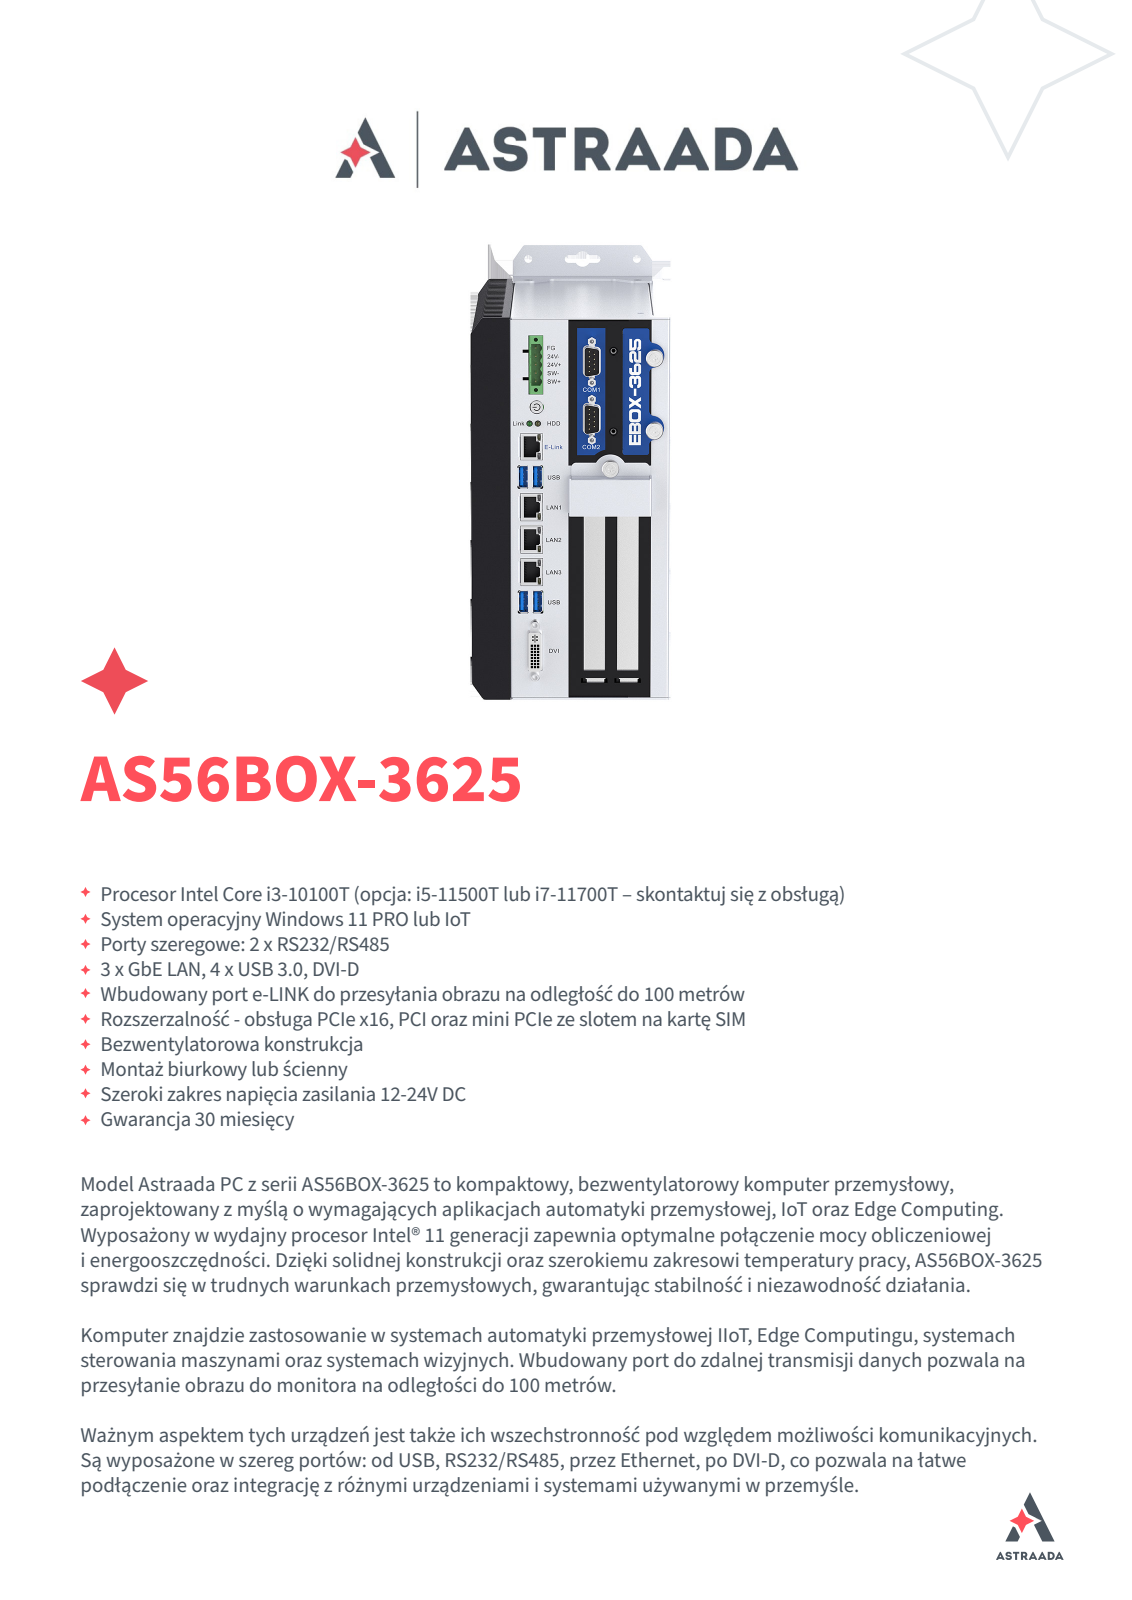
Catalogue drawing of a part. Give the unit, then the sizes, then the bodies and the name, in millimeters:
Units: millimetres
Overall size (bounding box): 278 × 206.7 × 120
Round holes (diameter × count): ⌀2 ×78, ⌀2.5 ×5, ⌀2.6 ×4, ⌀5 ×4, ⌀8 ×4, ⌀4 ×3, ⌀3 ×2, ⌀3.5 ×2, ⌀4.5 ×2, ⌀3.2 ×1, ⌀3.8 ×1, ⌀6.69 ×1
Round bosses / shafts (diameter × count): ⌀1 ×18, ⌀4.5 ×2, ⌀3 ×2, ⌀8 ×1, ⌀7.5 ×1, ⌀7 ×1, ⌀6.23 ×1
Partial cylindrical surfaces — rounded edges, fillets, slot ends (radius × count): R1 ×80, R0.3 ×60, R2 ×20, R1.4 ×14, R2.5 ×12, R1.7 ×10, R3 ×10, R0.5 ×9
Main face-to-face distances: 6, 18, 12, 24, 30, 36, 42, 48, 54, 60
Hole centre spacings: 6.93, 10.58, 8, 4, 13.86, 4.01, 14.42, 16
Bodies: 0 solids, 1591 faces (847 planar, 696 cylindrical, 48 other)
Part name (STEP PRODUCT): EBOX-3625
STEP written by: SolidWorks 2016 (AUTOMOTIVE_DESIGN)
